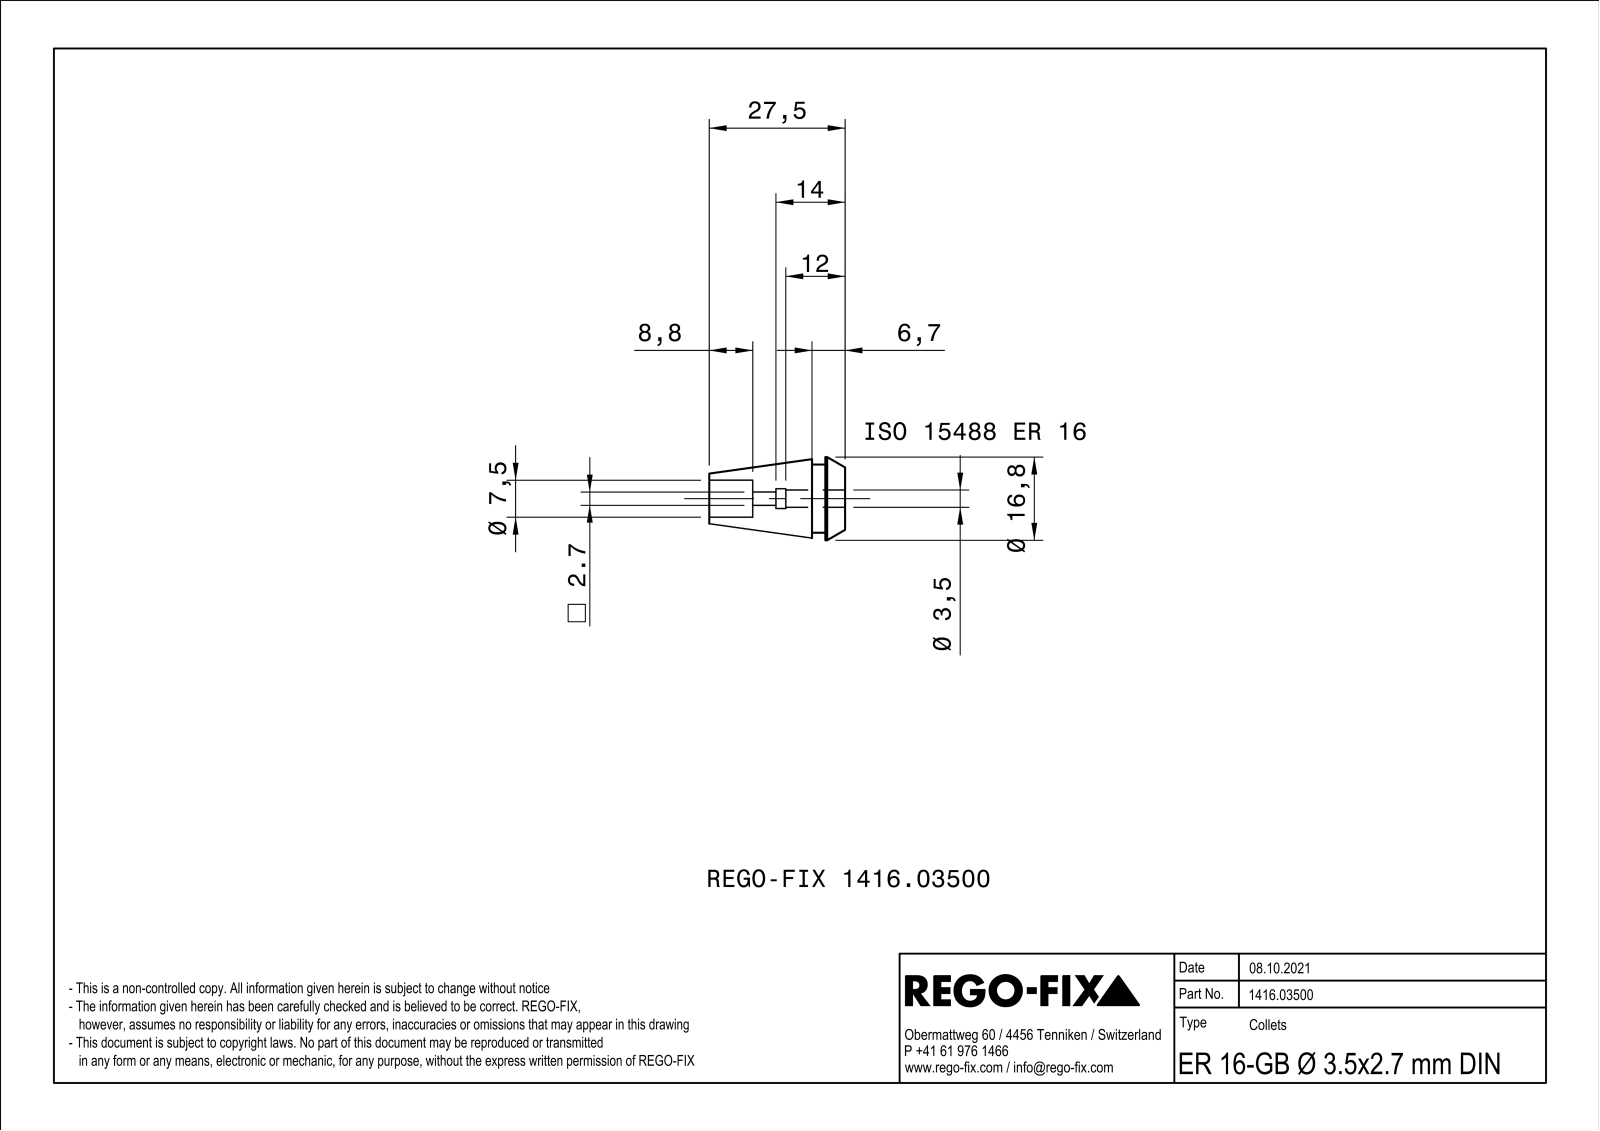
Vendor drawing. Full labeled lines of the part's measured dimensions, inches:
Part name (STEP PRODUCT): NOCUT
STEP written by: SIEMENS PLM Software Solid Edge ST10 (AUTOMOTIVE_DESIGN)
Units: inches
Bodies: 1 solid, 164 faces (72 planar, 32 cylindrical, 60 other)
Overall size (bounding box): 1.083 × 0.661 × 0.661
Volume: 0.176 in³ · Surface area: 5.158 in²
Round holes (diameter × count): ⌀0.295 ×1
Round bosses / shafts (diameter × count): ⌀0.661 ×1, ⌀0.543 ×1
Partial cylindrical surfaces — rounded edges, fillets, slot ends (radius × count): R0.061 ×1, R0.069 ×1, R0.079 ×1
Main face-to-face distances: 0.024, 0.157, 0.264, 0.106, 1.083, 0.925, 0.819, 0.044, 0.068, 0.177
